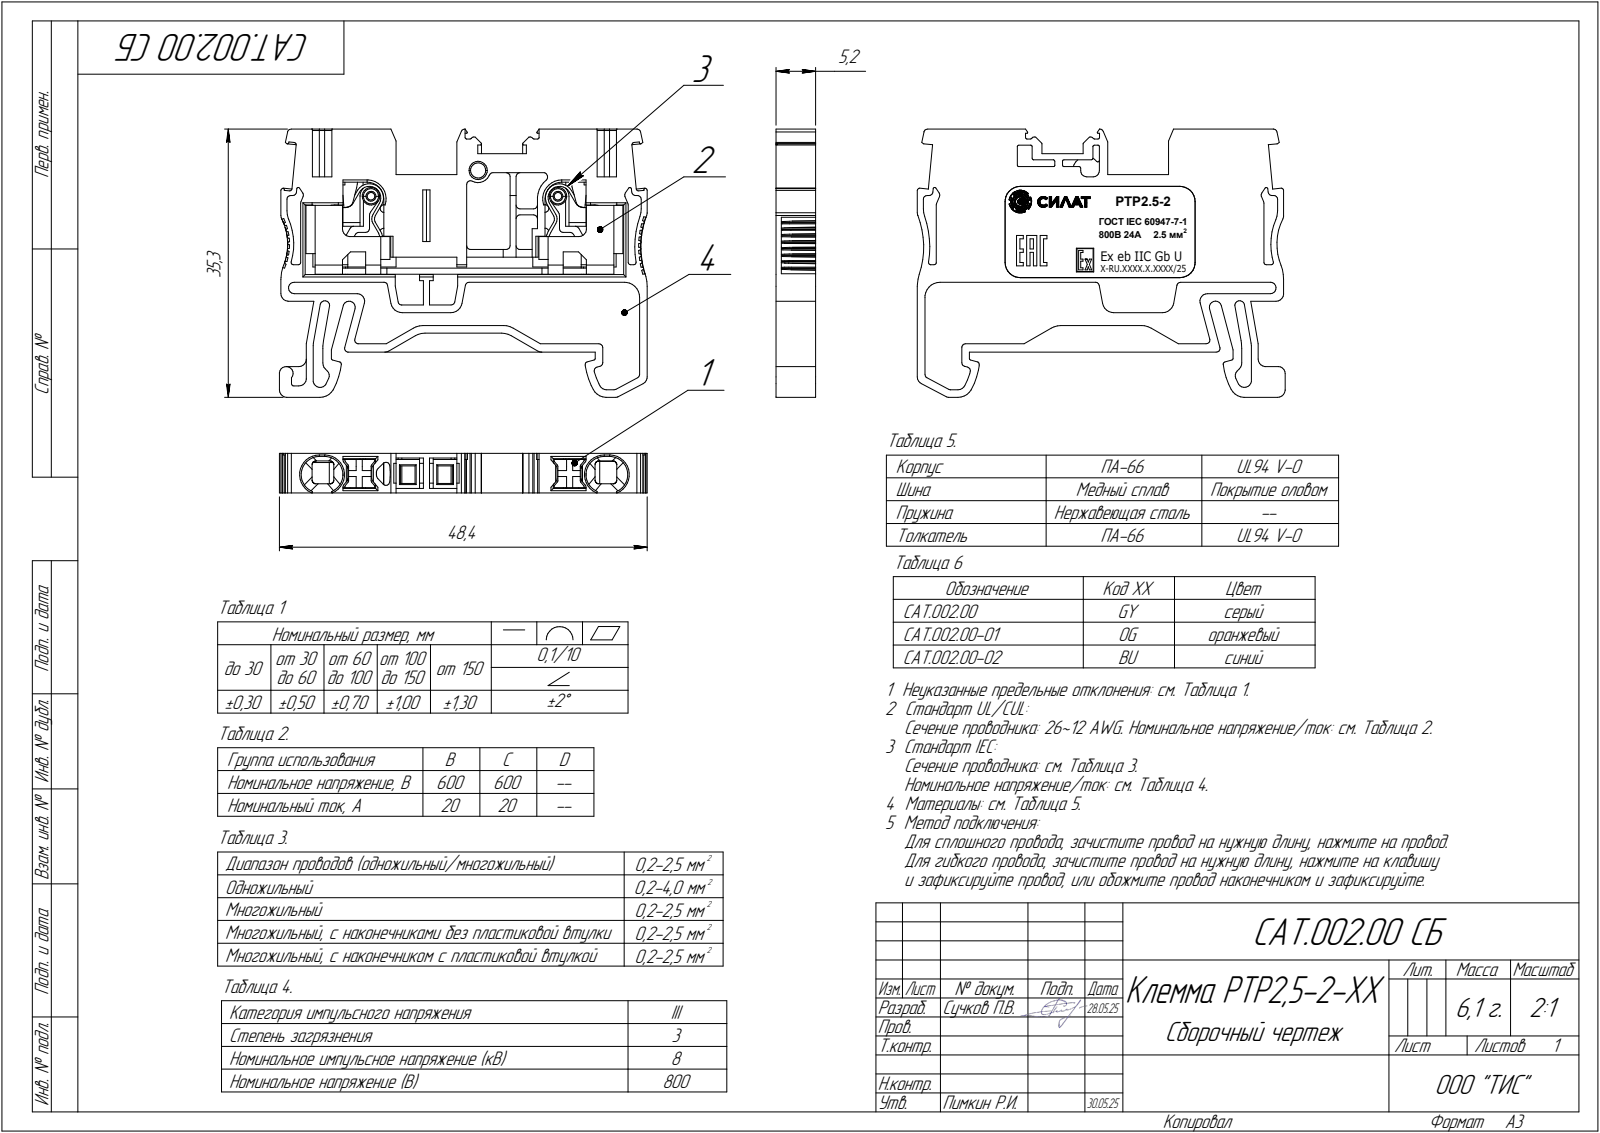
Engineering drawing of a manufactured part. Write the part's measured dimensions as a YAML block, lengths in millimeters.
part_name: "Клемма PTP2,5-2-XX"
step_written_by: "SolidWorks 2024 (AUTOMOTIVE_DESIGN)"
units: millimeters
bodies: {solids: 1, faces: 448, planar: 294, cylindrical: 149, other: 5}
overall_size: [48.4, 35.3, 5.2]
volume: 6425
surface_area: 4259
partial_cylinders:
  - {radius: 0.15, count: 36}
  - {radius: 0.3, count: 25}
  - {radius: 0.5, count: 25}
  - {radius: 1, count: 8}
  - {radius: 0.2, count: 7}
  - {radius: 2.4, count: 4}
  - {radius: 2, count: 3}
  - {radius: 5, count: 3}
face_to_face_distances: [5.2, 0.6, 4.2, 29.35, 0.9, 4.6, 1, 2.5, 26.85, 0.4]
